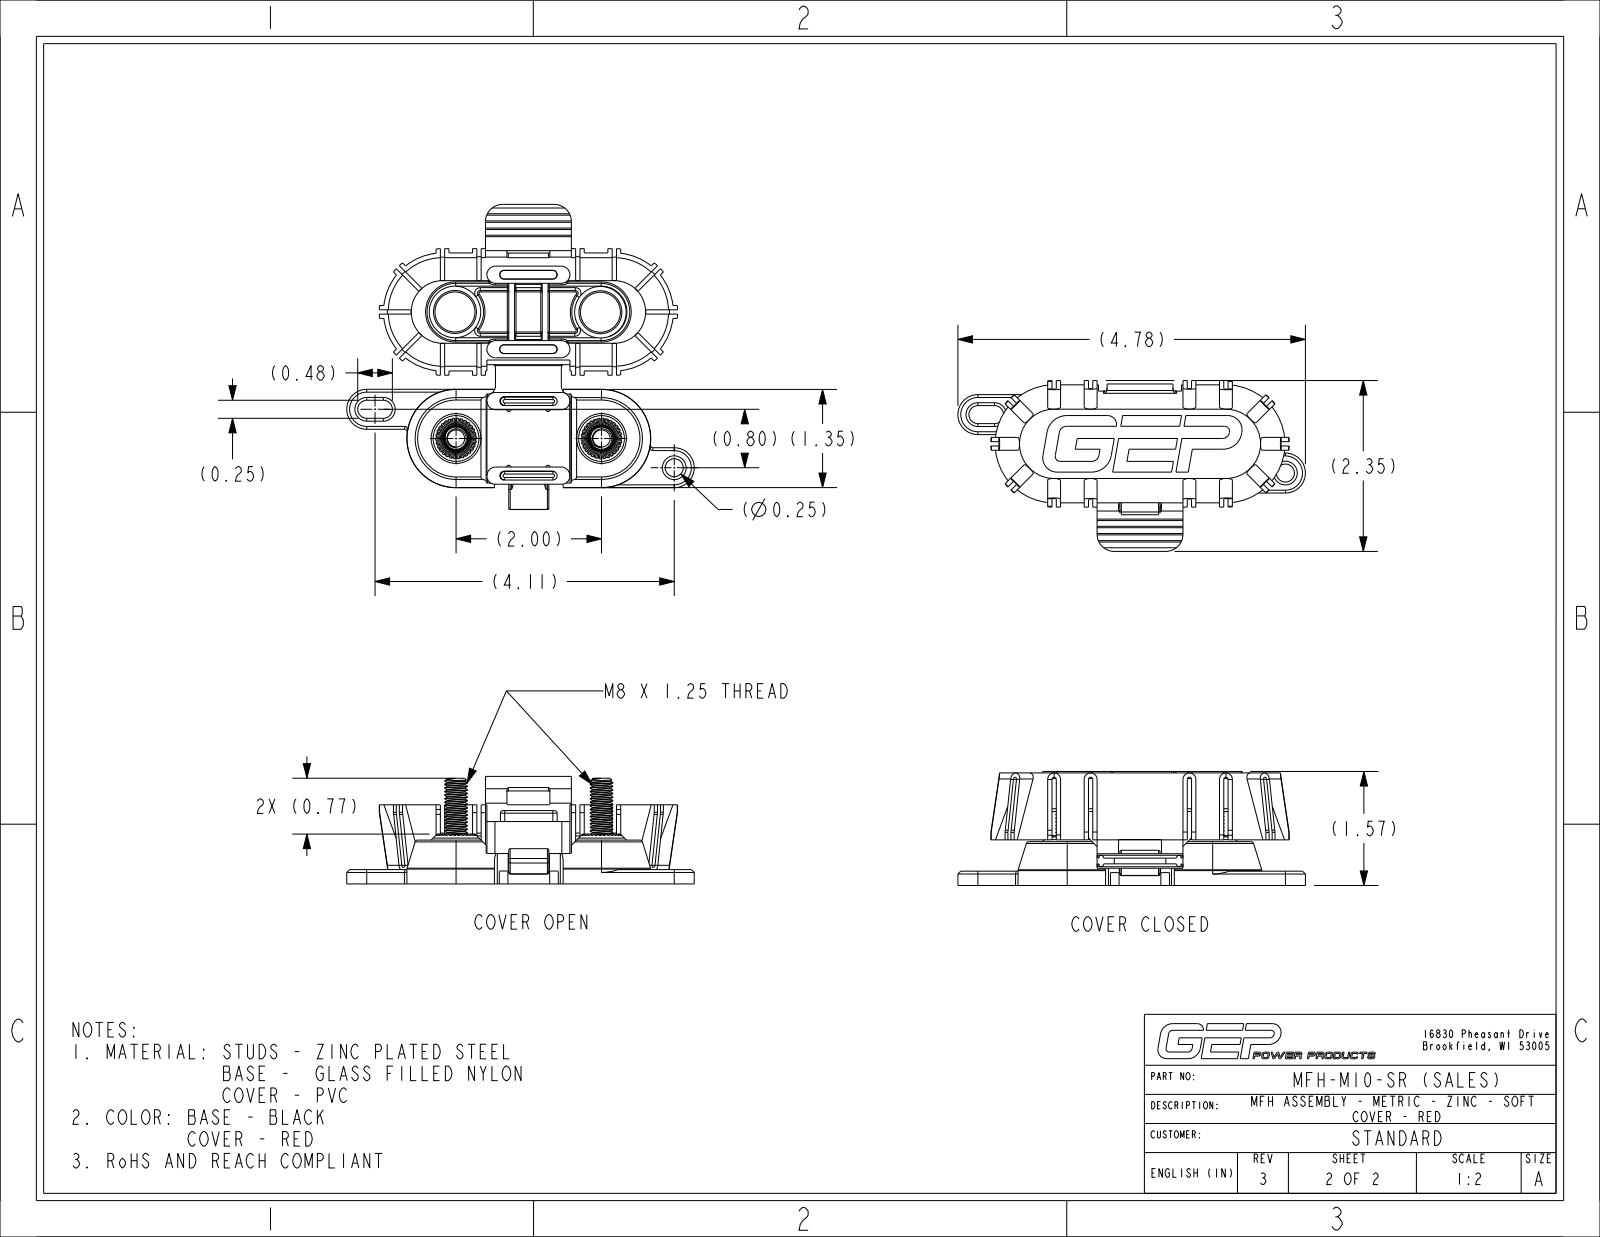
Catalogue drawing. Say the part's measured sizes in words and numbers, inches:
The part is named "MFH-MXX-XX_BODY_NCF; C05-1003-M1_NCF; MFH-SR_NCF_INSTALLED; MFH-M10-SR_INSTALLED_NCF_ASM". Its 3-D file was written by "CREO PARAMETRIC BY PTC INC, 2024014 (CONFIG_CONTROL_DESIGN)". It is 4 solids with 2099 faces: 769 planar, 729 cylindrical and 601 other. Overall it measures 4.778 by 2.348 by 1.567 inches. Its volume is 3.169 cubic inches and its surface area 83.8 square inches. Round holes: 2 of diameter 0.354, 2 of diameter 0.591, 1 of diameter 0.248. Round bosses or shafts: 2 of diameter 0.63, 2 of diameter 0.315. Partial cylindrical surfaces (rounded edges, fillets, slot ends): 236 of radius 0.016, 24 of radius 0.02, 20 of radius 0.039, 14 of radius 0.02, 13 of radius 0.015, 10 of radius 0.012, 10 of radius 0.035, 10 of radius 0.059. The main face-to-face distances are 0.059, 0.118, 0.079, 0.423, 0.177, 0.945, 1.024, 1.13, 0.02, 0.6. The hole center spacings are 2, 1.078, 1.087, 1.991, 2.009, 3.027, 3.036.
